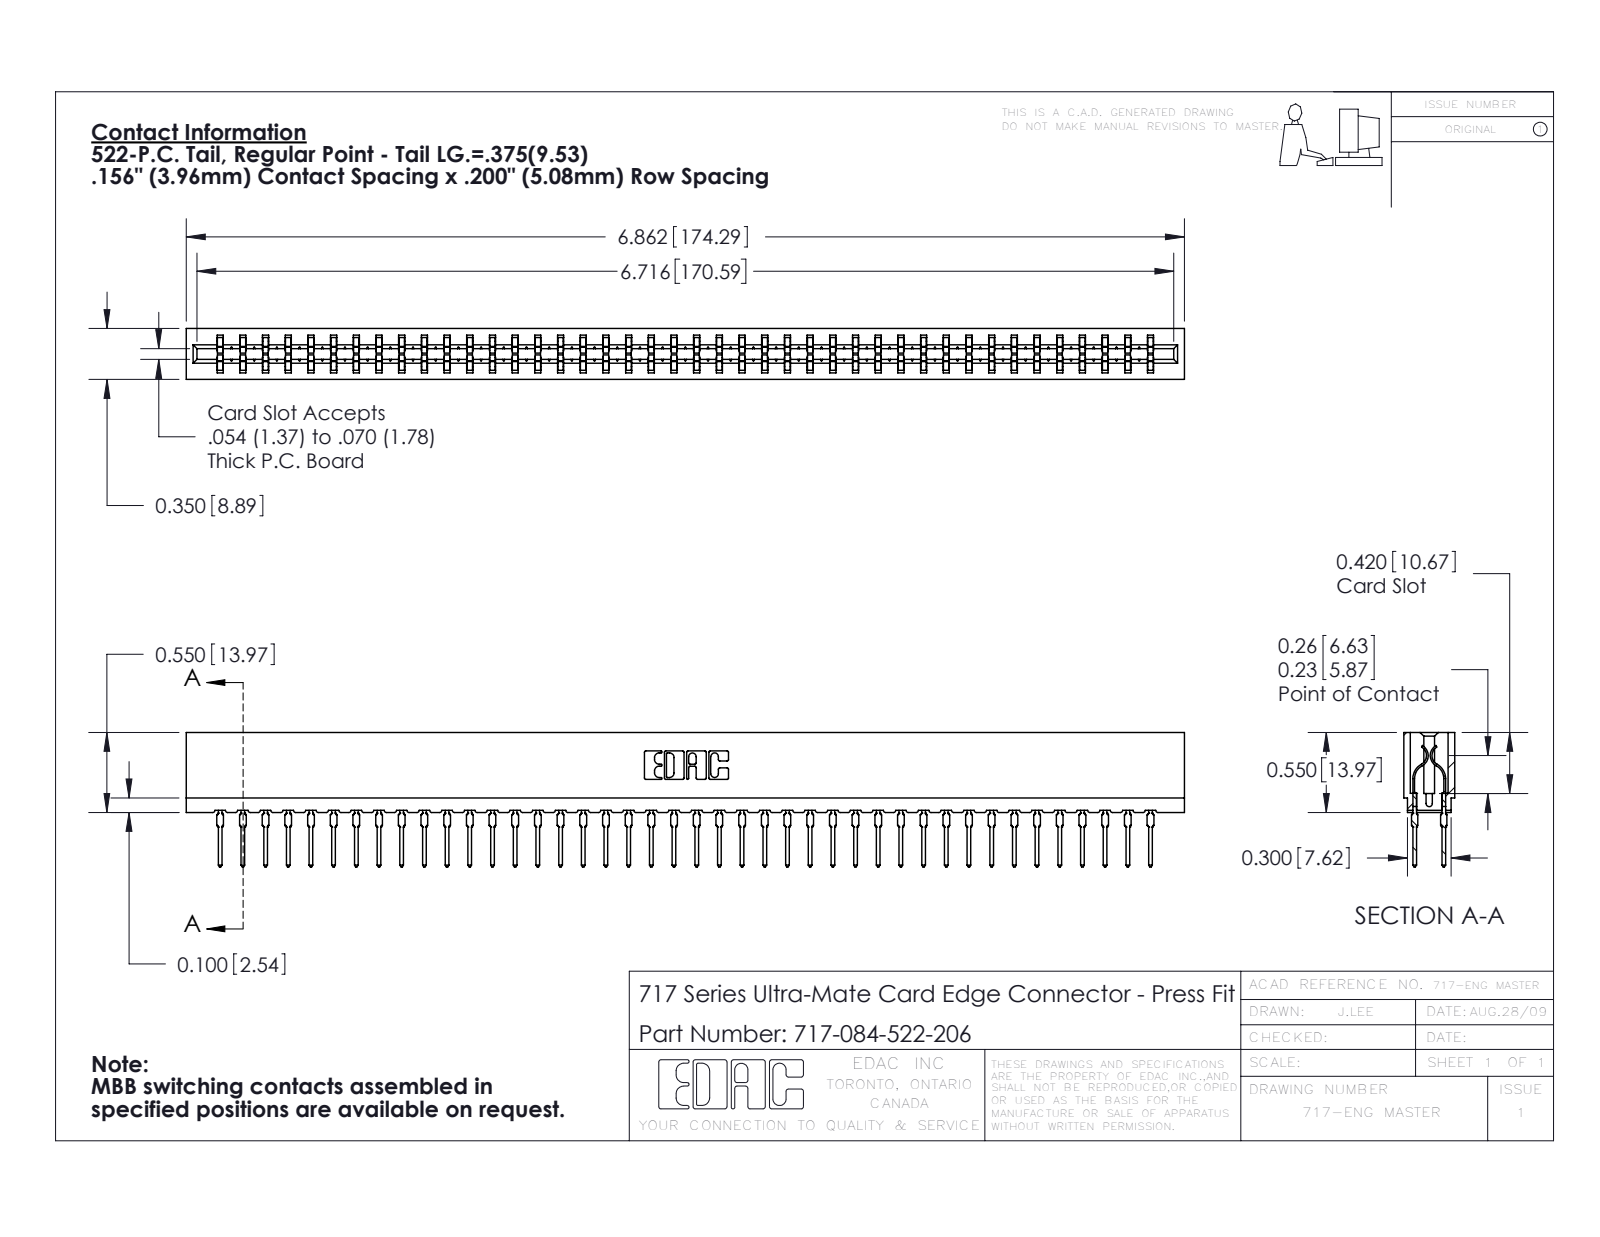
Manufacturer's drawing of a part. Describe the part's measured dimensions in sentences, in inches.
The part is named "745-292-001_522; 717-084-522-206; 717 Part_Insulator Option - 06". Its 3-D file was written by "SolidWorks 2016 (CONFIG_CONTROL_DESIGN)". It is 85 solids with 7654 faces: 3960 planar, 1510 cylindrical and 2184 other. Overall it measures 6.862 by 0.924 by 0.35 inches. Its volume is 0.927 cubic inches and its surface area 36.54 square inches. Partial cylindrical surfaces (rounded edges, fillets, slot ends): 168 of radius 0.021, 84 of radius 0.015, 22 of radius 0.01, 8 of radius 0.005, 8 of radius 0.011, 6 of radius 0.007, 6 of radius 0.031, 3 of radius 0.026. The main face-to-face distances are 0.212, 0.138, 0.35, 0.063, 0.287, 0.076, 0.149, 0.074, 0.045, 0.305.
